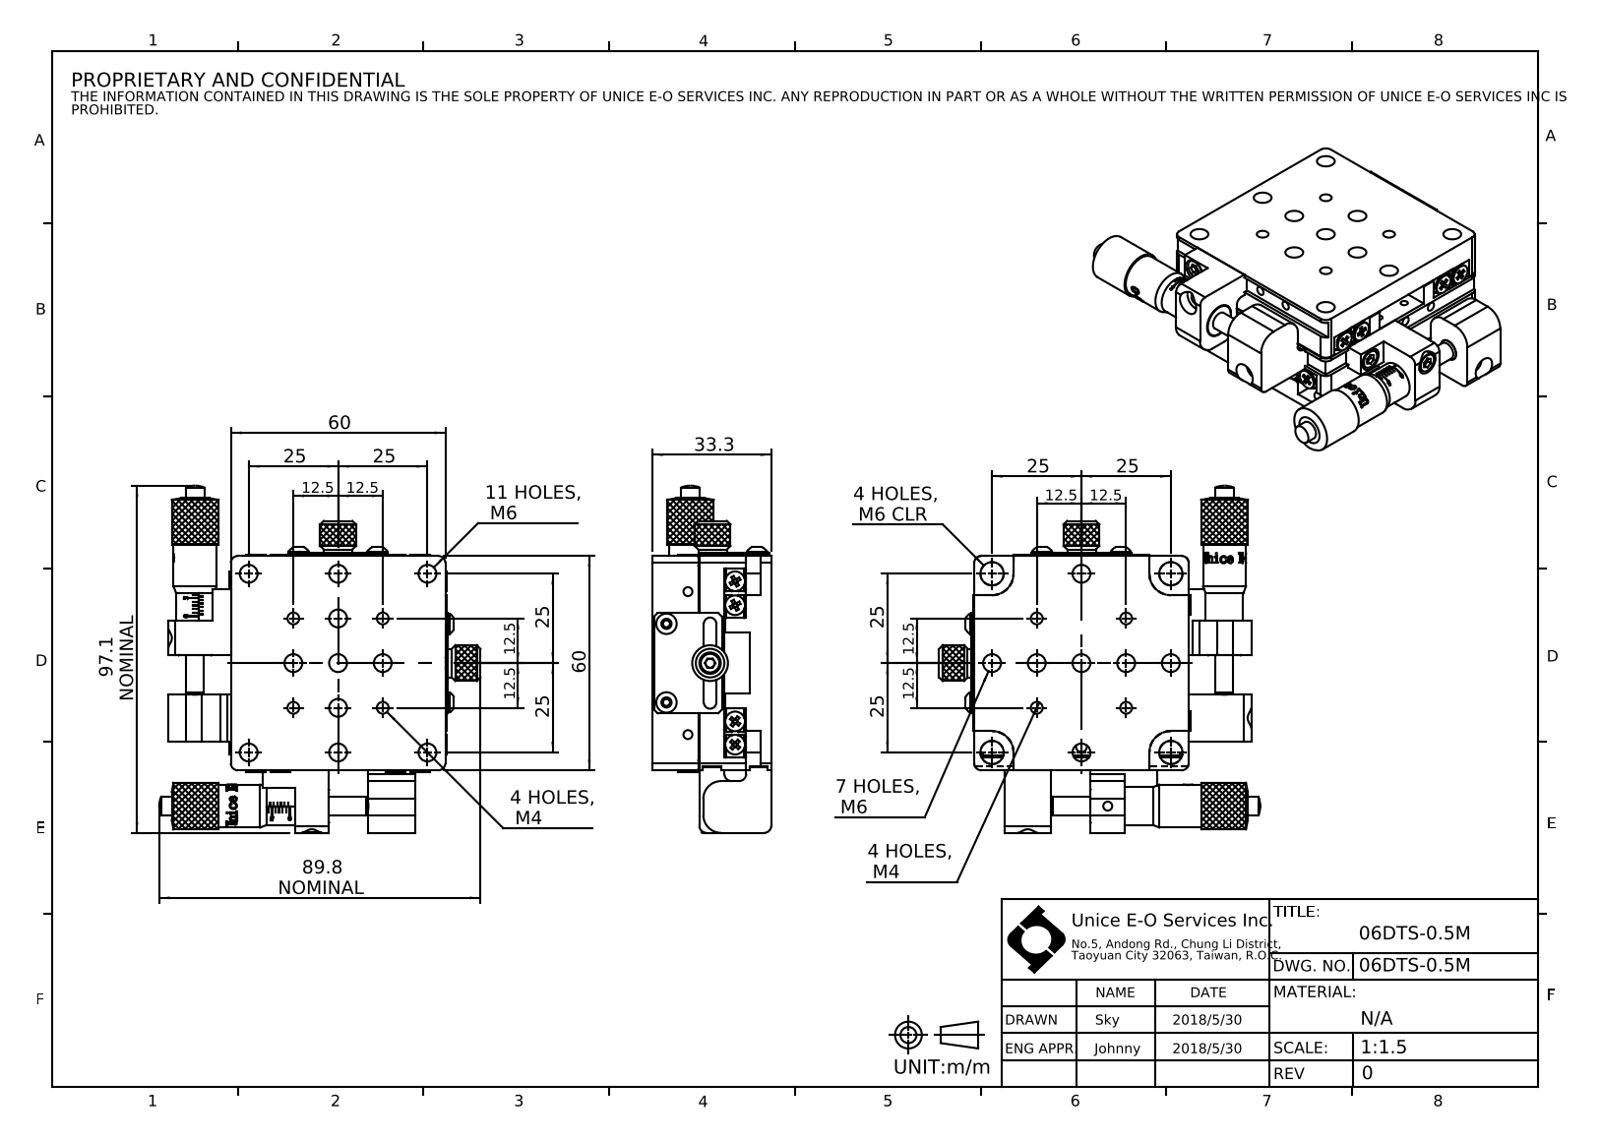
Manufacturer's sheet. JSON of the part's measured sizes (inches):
{"part_name": "06DTS-0.5M", "step_written_by": "SolidWorks 2016 (AUTOMOTIVE_DESIGN)", "units": "inches", "bodies": {"solids": 0, "faces": 1107, "planar": 645, "cylindrical": 277, "other": 185}, "overall_size": [3.825, 3.535, 1.311], "round_holes": [[0.098, 16], [0.197, 14], [0.256, 10], [0.081, 8], [0.13, 4], [0.236, 3], [0.118, 2], [0.374, 2], [0.134, 1], [0.417, 1]], "round_bosses_or_shafts": [[0.217, 11], [0.224, 4], [0.512, 2], [0.472, 2], [0.413, 2], [0.394, 2], [0.315, 2], [0.205, 2]], "partial_cylinders_radius": [[0.079, 10], [0.197, 8], [0.069, 4], [0.236, 4], [0.235, 2]], "face_to_face_distances": [0.516, 0.52, 0.276, 0.24, 0.791, 0.28, 0.795, 1.311, 1.035, 0.236], "hole_center_spacings": [1.1, 0.696, 0.984, 0.394, 0.492, 1.556, 1.392, 2.017]}
